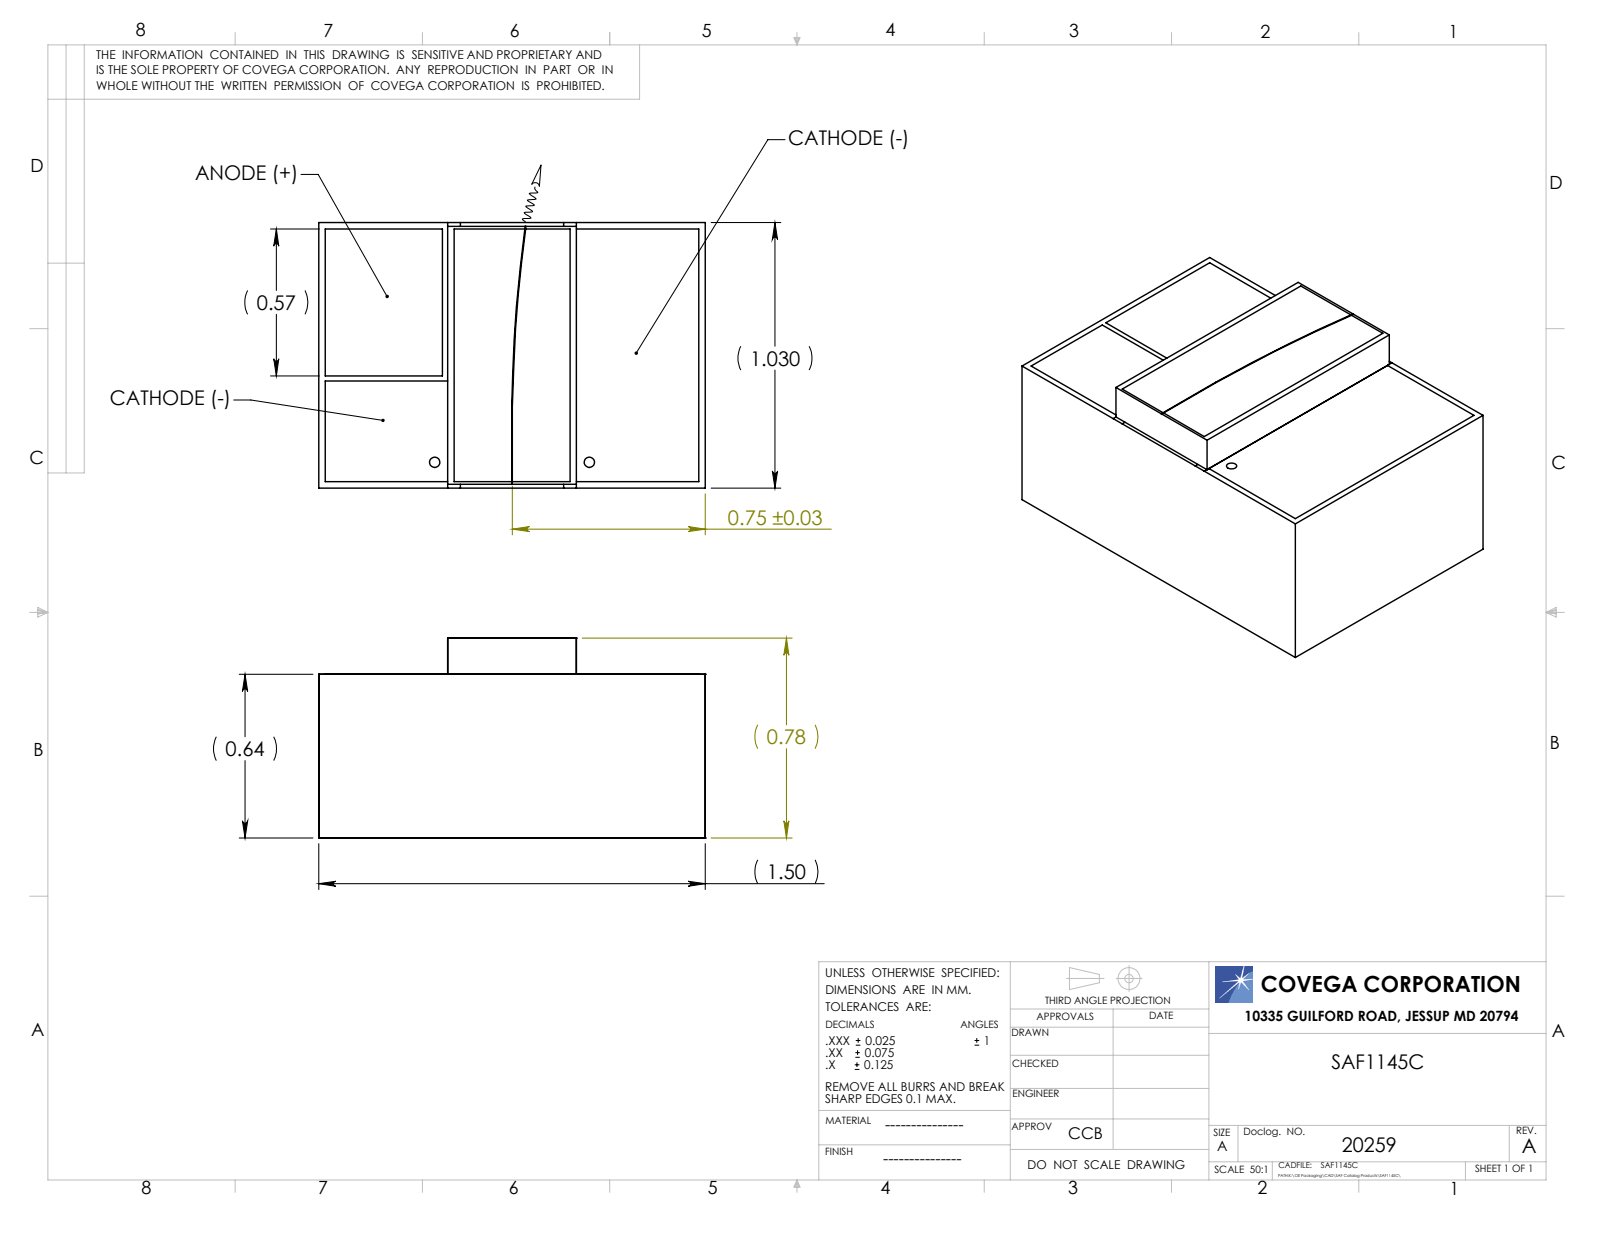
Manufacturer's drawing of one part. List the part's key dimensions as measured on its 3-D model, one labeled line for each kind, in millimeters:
Part name (STEP PRODUCT): 20259; 31151-XXX; 32068-000
STEP written by: SolidWorks 2009 (AUTOMOTIVE_DESIGN)
Units: millimetres
Bodies: 2 solids, 26 faces (26 planar, 0 cylindrical, 0 other)
Overall size (bounding box): 1.5 × 1.03 × 0.78
Volume: 1 mm³ · Surface area: 8 mm²
Main face-to-face distances: 0.64, 1.03, 1.5, 0.78, 0.5, 1, 1.01, 1.02
